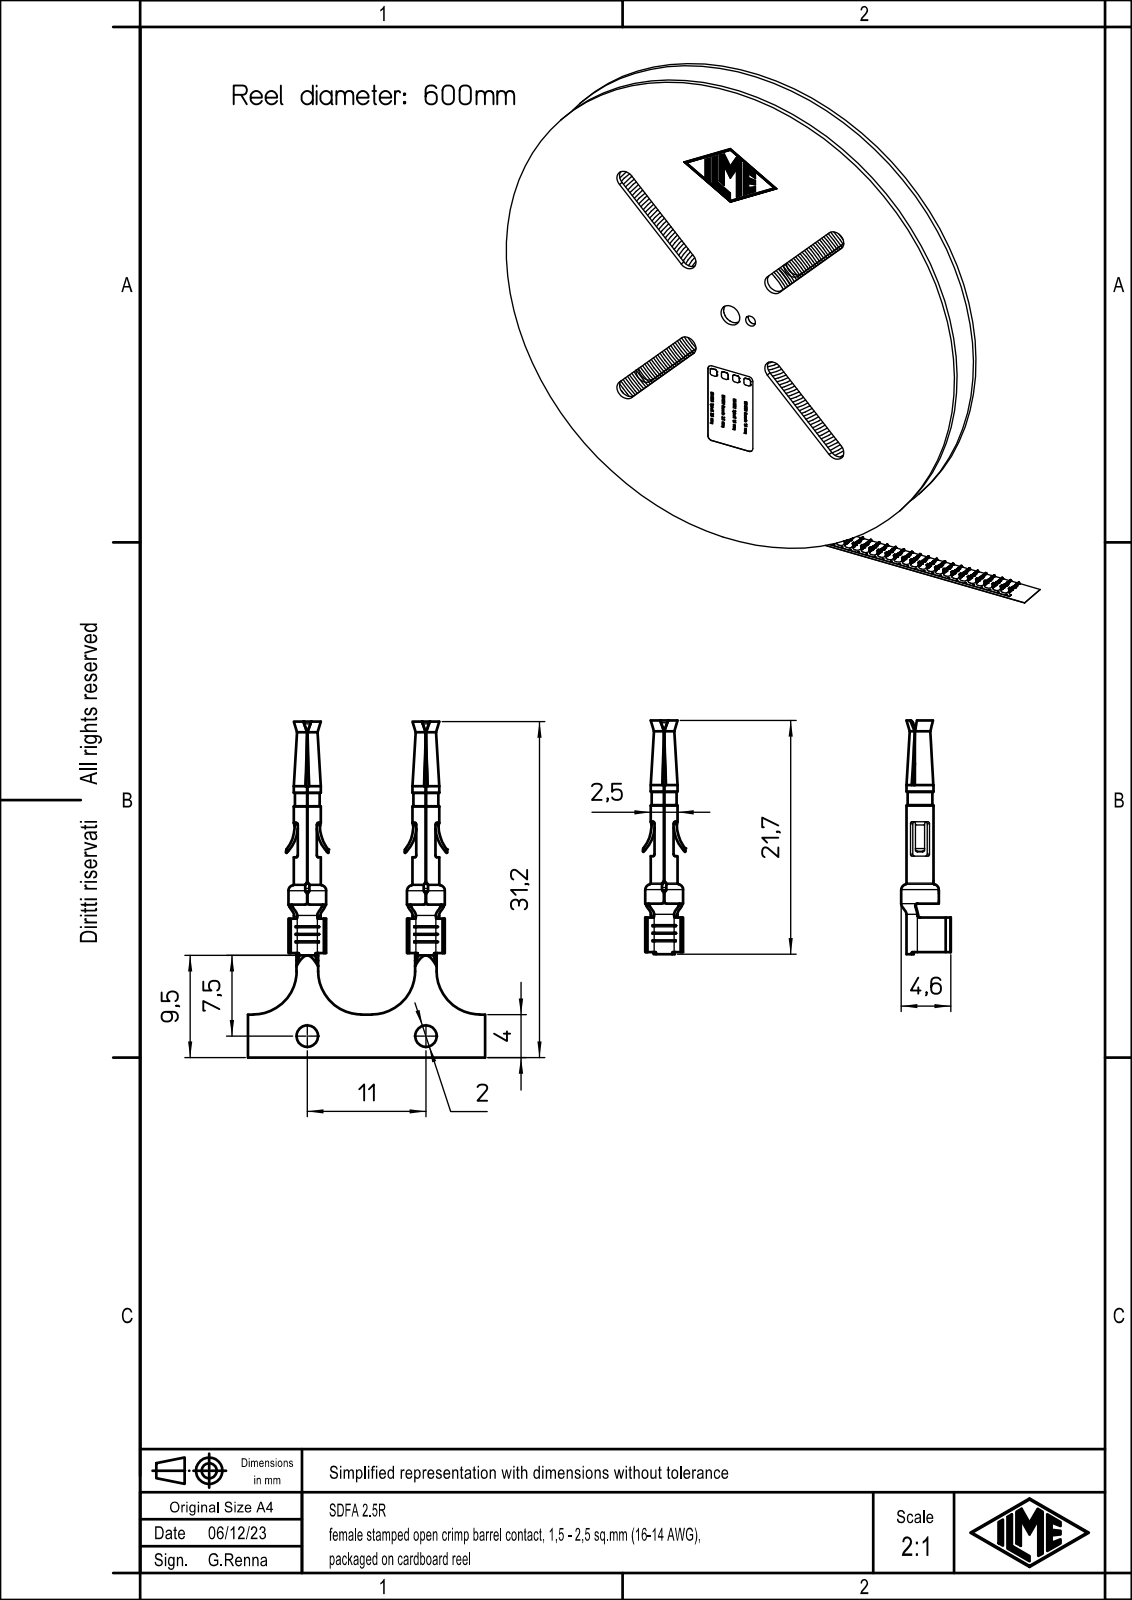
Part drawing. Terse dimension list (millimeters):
name: SDFA_2.5
written by: Creo Elements/Direct Modeling 20.1B 02-Apr-2019 (C) Parametric Technology GmbH (AUTOMOTIVE_DESIGN)
unit: mm
bodies: 1 solid, 216 faces (68 planar, 83 cylindrical, 65 other)
size: 21.7 × 4.6 × 3.97
volume: 42 mm³; area: 326 mm²
holes: 1× ⌀1.7, 1× ⌀1.9, 1× ⌀2.9
bosses: 1× ⌀3.5, 1× ⌀2.5, 1× ⌀2.3
rounds: 26× R0.2, 4× R3.5, 2× R0.1, 1× R1.05
face distances: 3.2, 4.5, 1.3, 0.85, 8.9, 5.7, 4.4, 3.4, 4.7, 9.1
